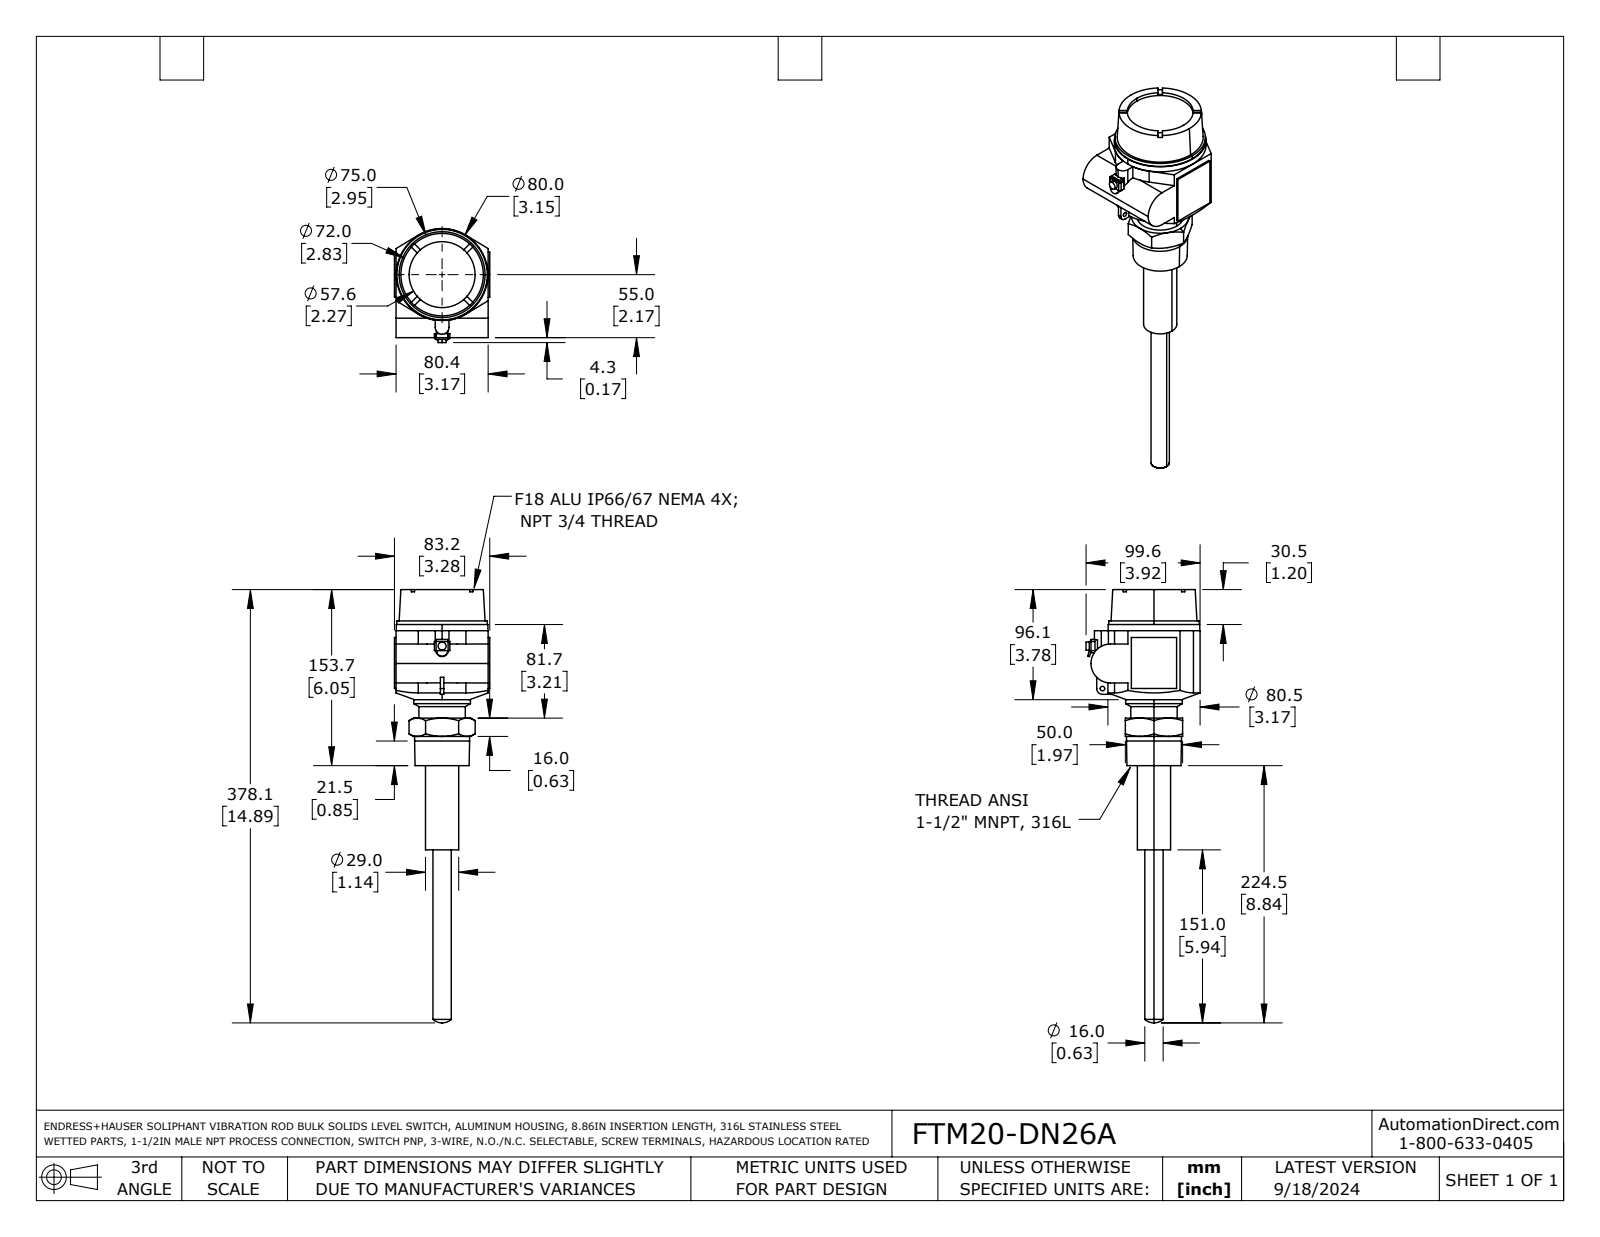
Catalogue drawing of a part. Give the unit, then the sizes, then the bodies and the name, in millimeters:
Units: millimetres
Overall size (bounding box): 378.2 × 99.5 × 83.2
Round holes (diameter × count): ⌀4 ×1, ⌀57.6 ×1
Round bosses / shafts (diameter × count): ⌀80 ×1, ⌀79 ×1, ⌀49.5 ×1, ⌀48 ×1, ⌀40.5 ×1, ⌀29 ×1, ⌀16 ×1, ⌀7 ×1
Partial cylindrical surfaces — rounded edges, fillets, slot ends (radius × count): R1.5 ×3, R5 ×2, R6 ×1, R17 ×1, R40.3 ×1
Main face-to-face distances: 1.4, 81.8, 83.2, 80.4, 3, 50, 150.6, 153.6, 80.5, 41.5
Volume: 702 200 mm³ · Surface area: 64 120 mm²
Bodies: 1 solid, 151 faces (88 planar, 36 cylindrical, 27 other)
Part name (STEP PRODUCT): FTM20-DN26A
STEP written by: SolidWorks 2021 (AUTOMOTIVE_DESIGN)
